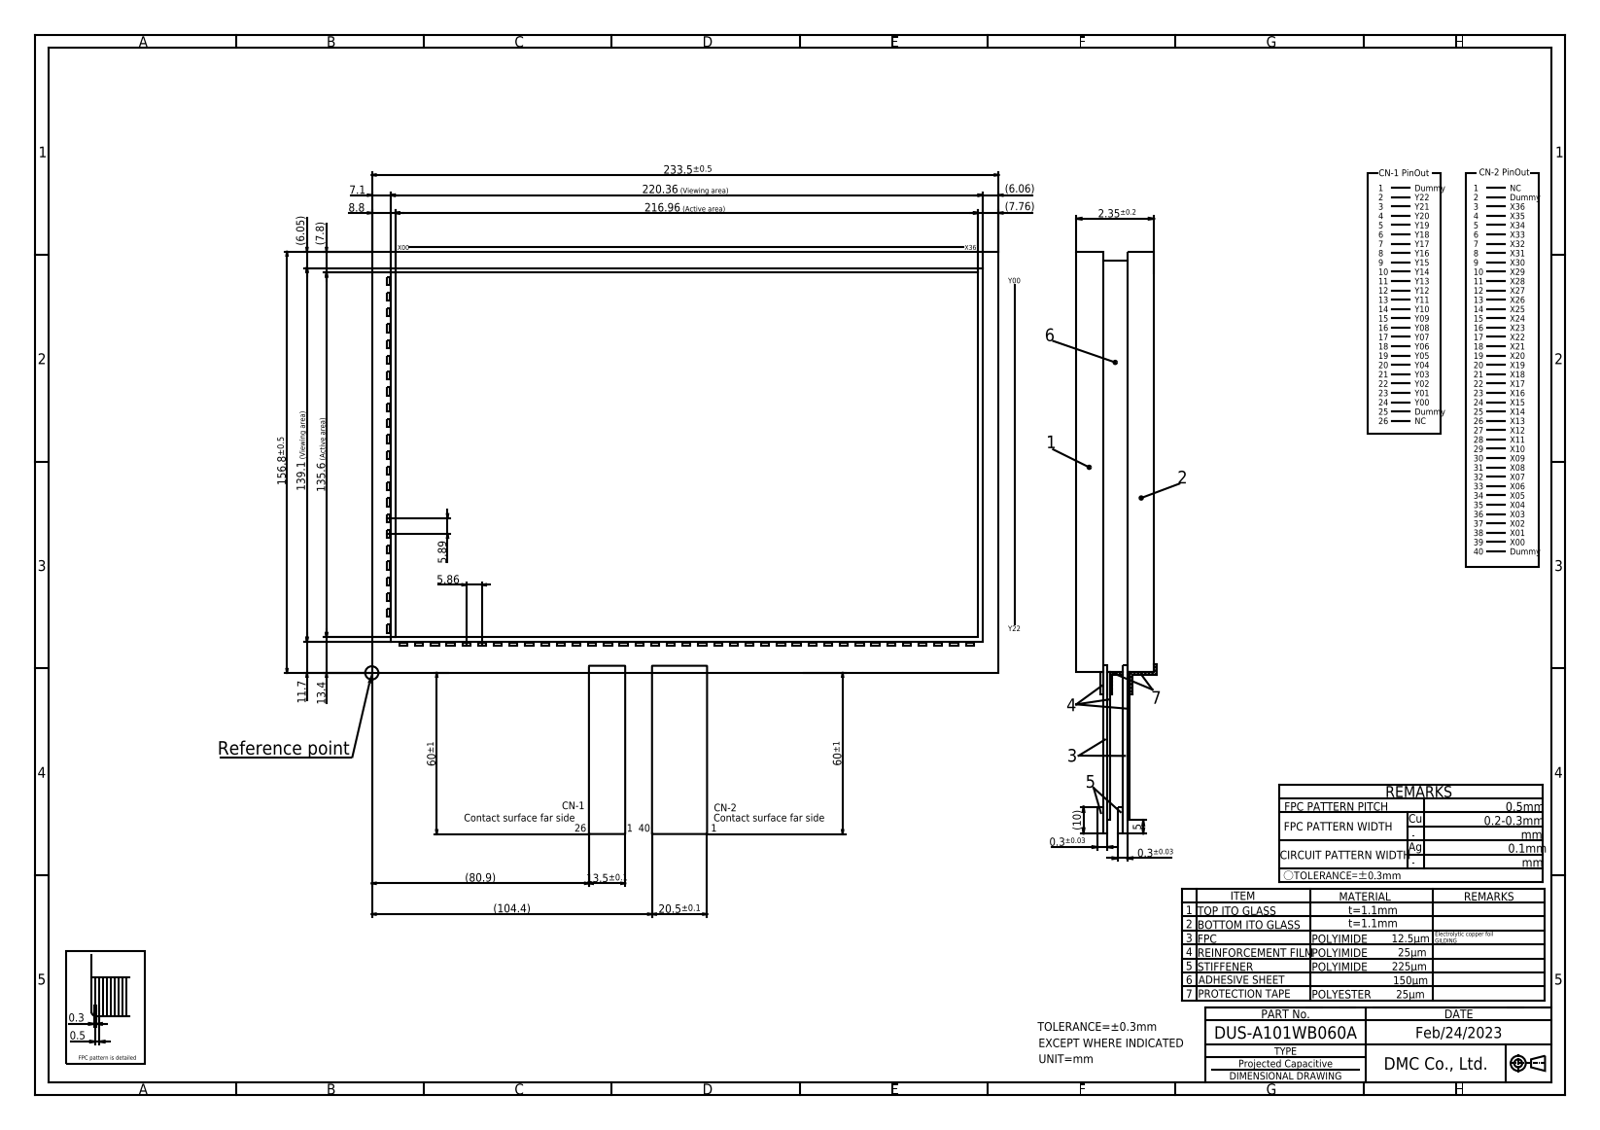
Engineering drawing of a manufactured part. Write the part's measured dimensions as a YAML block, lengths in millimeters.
part_name: "DUS-A101WB060A"
step_written_by: "Autodesk Inventor 2020 (CONFIG_CONTROL_DESIGN)"
units: millimeters
bodies: {solids: 1, faces: 302, planar: 298, cylindrical: 4, other: 0}
overall_size: [326.9, 248.16, 2.35]
volume: 86226
surface_area: 79345
partial_cylinders:
  - {radius: 0.2, count: 4}
face_to_face_distances: [2.35, 1.14, 1.21, 1.25, 1.1, 1.11, 1, 2.25, 156.8, 233.5]
